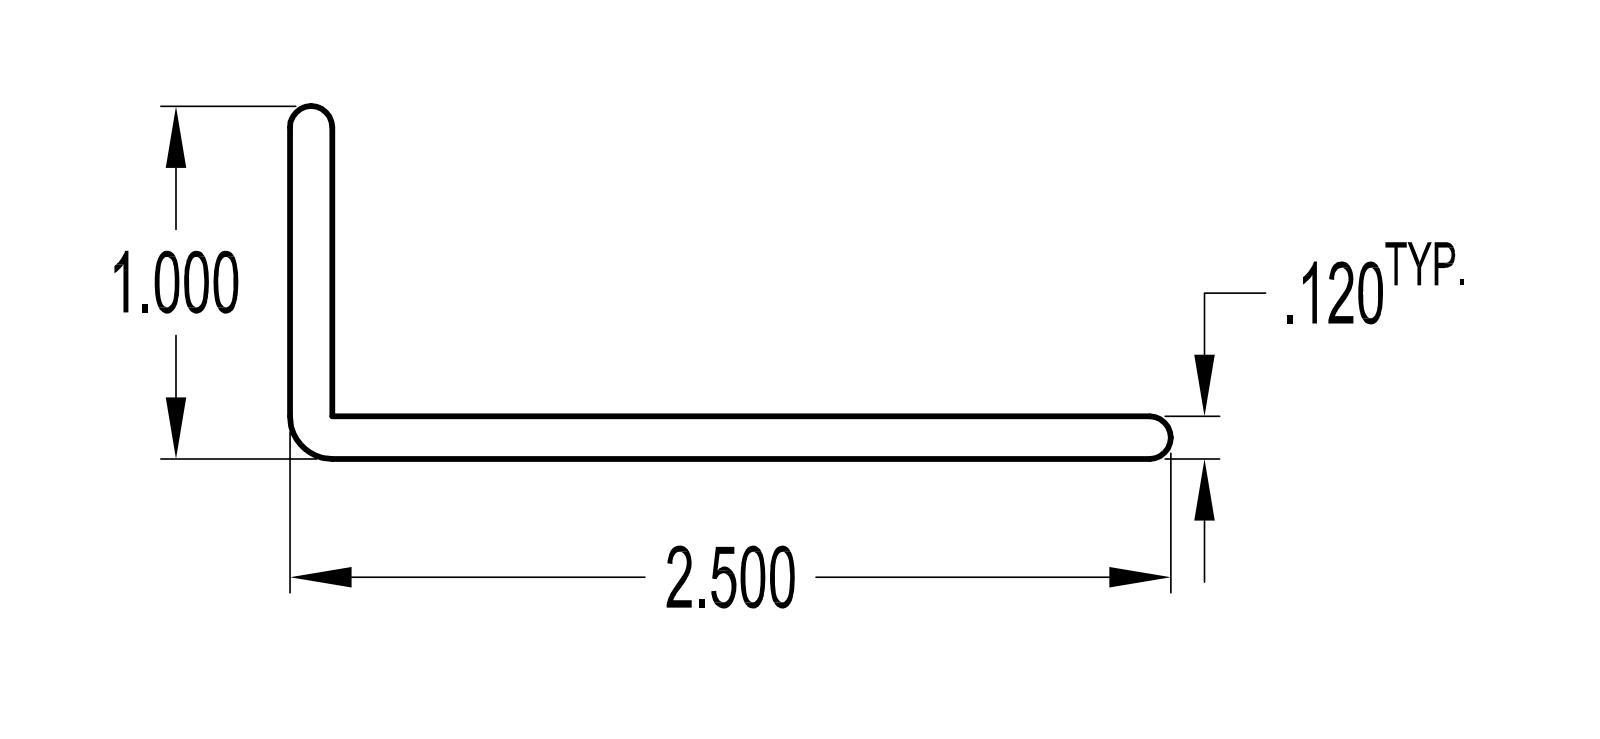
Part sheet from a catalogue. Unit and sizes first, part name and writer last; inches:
Units: inches
Overall size (bounding box): 6 × 2.5 × 1
Partial cylindrical surfaces — rounded edges, fillets, slot ends (radius × count): R0.06 ×2, R0.12 ×1
Main face-to-face distances: 0.12, 6
Volume: 2.397 in³ · Surface area: 41.87 in²
Bodies: 1 solid, 9 faces (6 planar, 3 cylindrical, 0 other)
STEP written by: KeyCreator Pro (AUTOMOTIVE_DESIGN)
